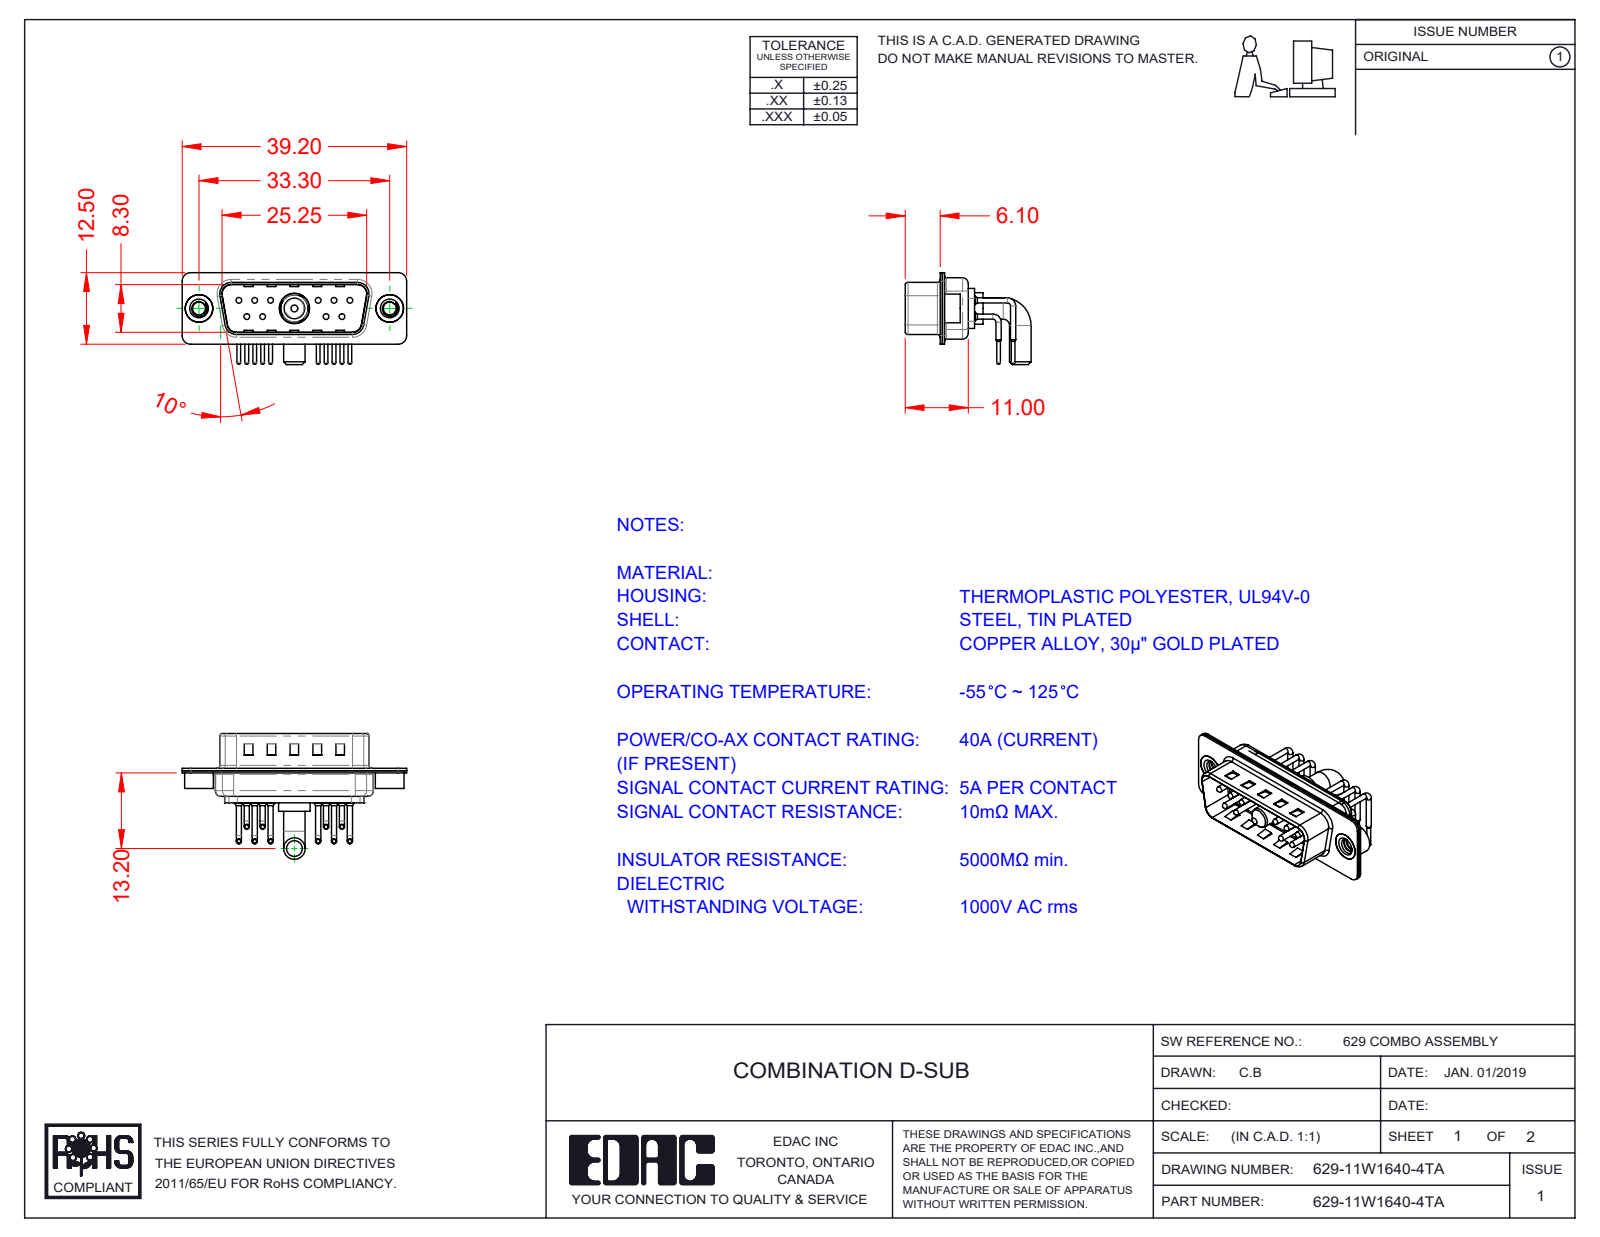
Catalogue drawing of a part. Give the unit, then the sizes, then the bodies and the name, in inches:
Units: inches
Overall size (bounding box): 1.543 × 0.865 × 0.632
Round holes (diameter × count): ⌀0.03 ×10, ⌀0.063 ×10, ⌀0.079 ×10, ⌀0.089 ×2, ⌀0.157 ×2, ⌀0.189 ×2, ⌀0.191 ×1, ⌀0.209 ×1
Round bosses / shafts (diameter × count): ⌀0.035 ×20, ⌀0.059 ×10, ⌀0.039 ×10, ⌀0.026 ×10, ⌀0.197 ×2, ⌀0.193 ×2, ⌀0.148 ×2, ⌀0.217 ×1
Partial cylindrical surfaces — rounded edges, fillets, slot ends (radius × count): R0.059 ×16, R0.079 ×12, R0.04 ×10, R0.02 ×8, R0.063 ×8, R0.039 ×7, R0.01 ×4, R0.024 ×4
Main face-to-face distances: 0.016, 0.031, 0.374, 0.358, 0.343, 0.39, 0.03, 0.047, 0.22, 0.014
Hole centre spacings: 0.124, 0.109, 0.545, 0.436, 0.654, 0.198, 0.198, 0.218
Volume: 0.13 in³ · Surface area: 8.179 in²
Bodies: 17 solids, 1496 faces (798 planar, 518 cylindrical, 180 other)
Part name (STEP PRODUCT): 629Combo Shell Front_15 Contacts; 629Combo Contact Row 2; 629Combo Contact Row 1; Power Pin_40A RA (+4 more)
STEP written by: SolidWorks 2020 (CONFIG_CONTROL_DESIGN)
